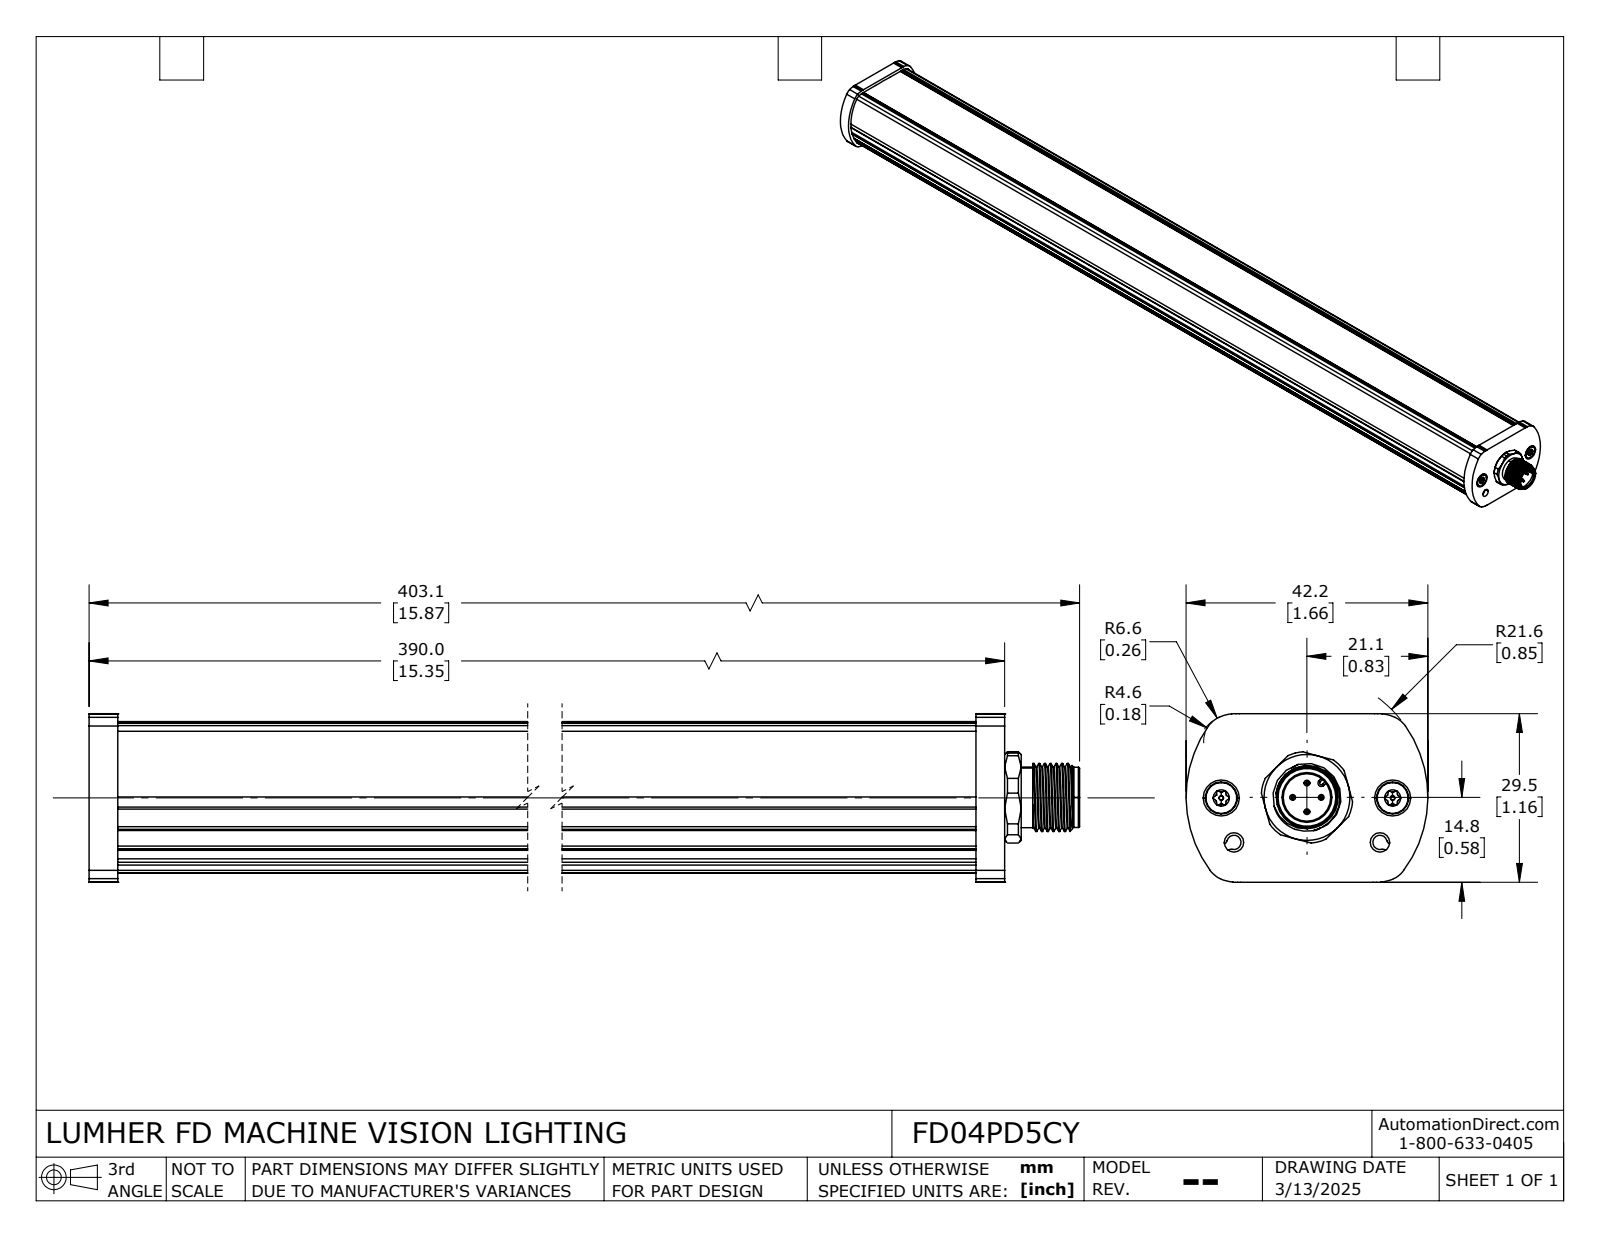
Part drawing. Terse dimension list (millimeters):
name: FD04PD5CY
written by: SolidWorks 2024 (AUTOMOTIVE_DESIGN)
unit: mm
bodies: 1 solid, 662 faces (97 planar, 383 cylindrical, 182 other)
size: 403.39 × 42.21 × 36.52
volume: 331 369 mm³; area: 83 633 mm²
holes: 8× ⌀3.4, 4× ⌀1.45, 1× ⌀8.3, 1× ⌀9, 1× ⌀9.4
bosses: 4× ⌀5.6, 4× ⌀3, 4× ⌀1.4, 4× ⌀1, 4× ⌀0.8, 1× ⌀11.9, 1× ⌀10.6, 1× ⌀10.5
rounds: 48× R0.57, 24× R0.25, 12× R0.8, 10× R3, 8× R3.1, 8× R4.6, 8× R5.1, 8× R6.6
face distances: 2.5, 5, 7.5, 10, 12.5, 4, 15, 2, 388.07, 17.5
hole spacings: 14.96, 2.5, 3.54, 8.06, 12.46, 15.18, 17.46, 25.5
